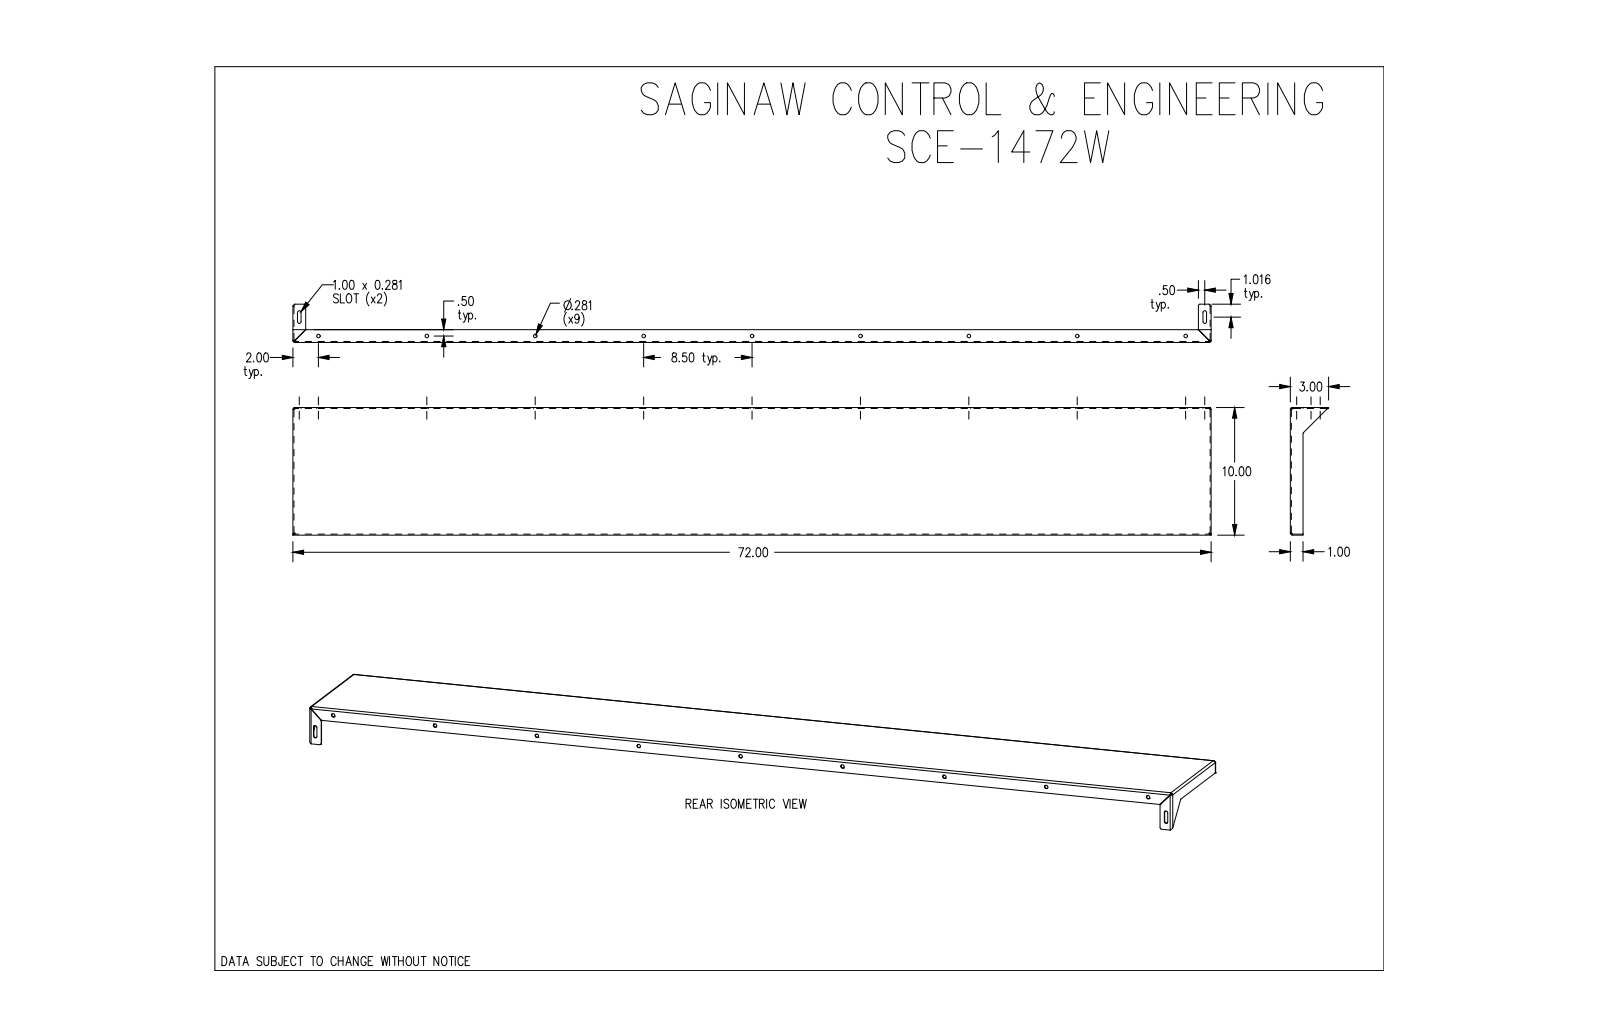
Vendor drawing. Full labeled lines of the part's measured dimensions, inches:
Part name (STEP PRODUCT): SCE-1472W
STEP written by: SolidWorks 2019 (AUTOMOTIVE_DESIGN)
Units: inches
Bodies: 1 solid, 49 faces (28 planar, 19 cylindrical, 2 other)
Overall size (bounding box): 72 × 10 × 3
Volume: 43.76 in³ · Surface area: 1 759 in²
Round holes (diameter × count): ⌀0.281 ×9
Partial cylindrical surfaces — rounded edges, fillets, slot ends (radius × count): R0.141 ×4, R0.106 ×2, R0.156 ×2, R0.125 ×1
Main face-to-face distances: 0.05, 9.95, 10, 9.9, 71.95, 72, 71.9, 0.95, 1, 9.94
Hole centre spacings: 8.5, 17, 25.5, 34, 42.5, 51, 8.498, 16.998
